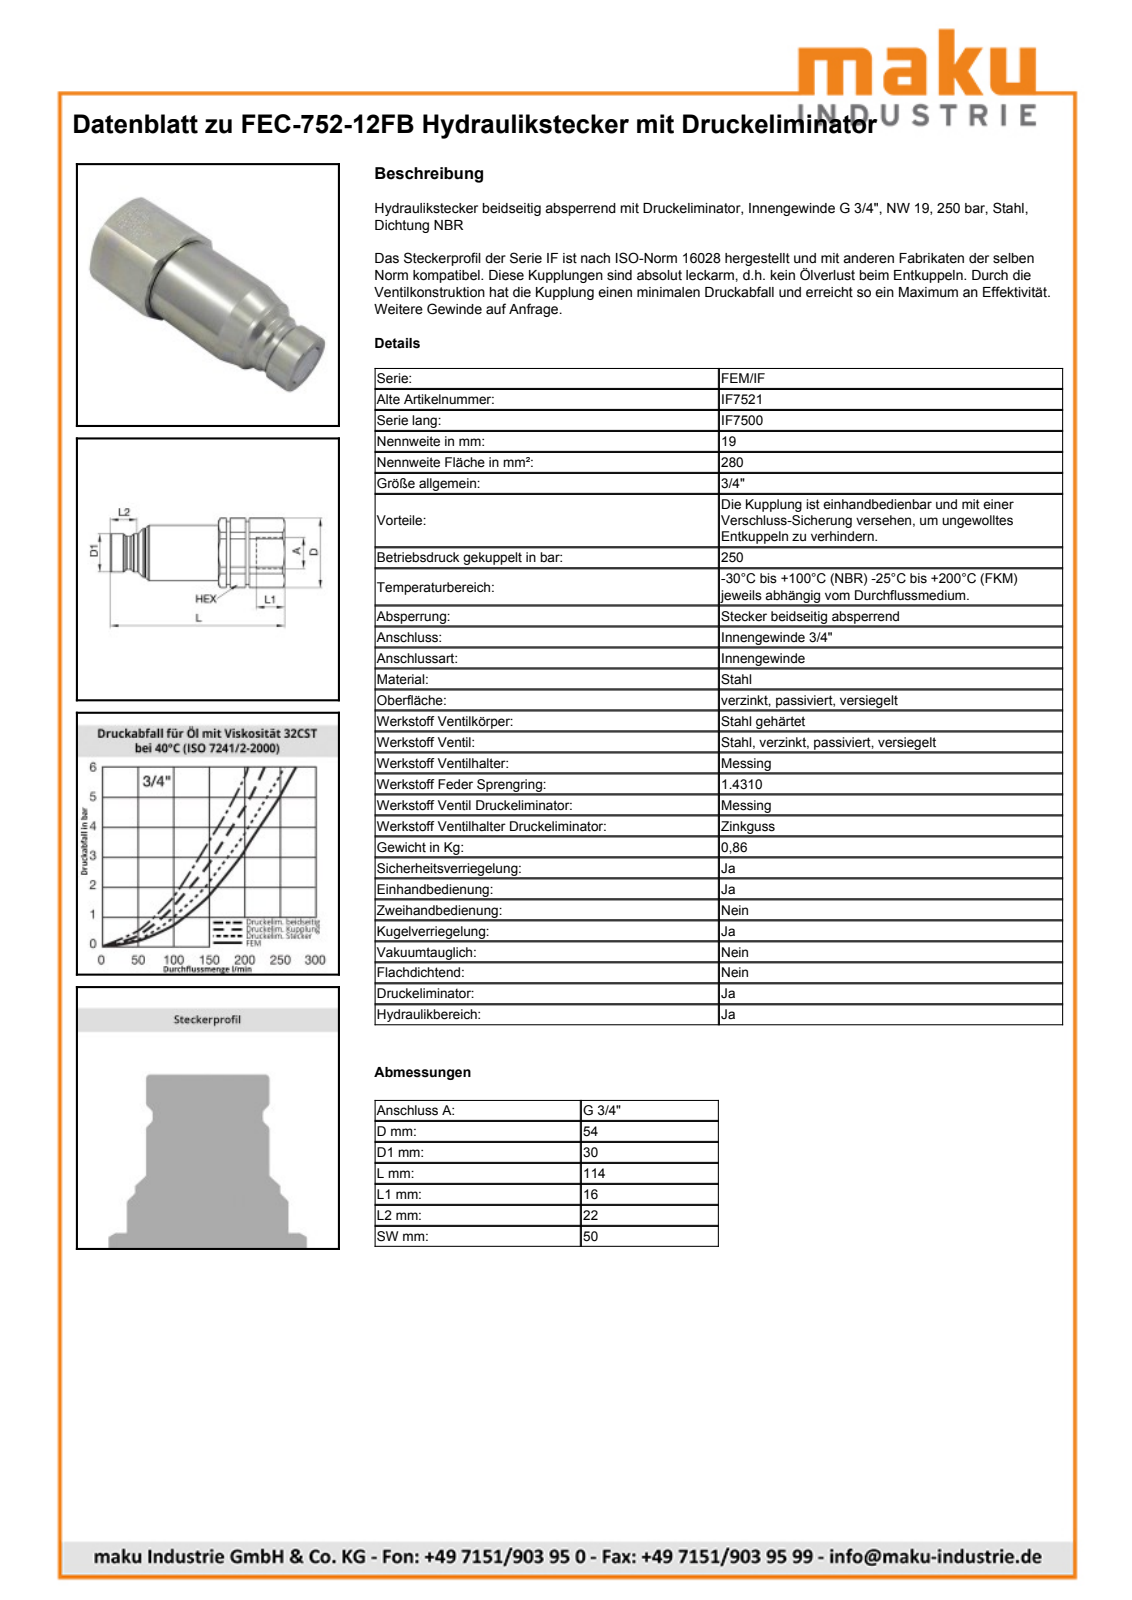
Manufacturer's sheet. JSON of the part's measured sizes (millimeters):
{"part_name": "FEC-752-12FB", "step_written_by": "SolidWorks 2009 (AUTOMOTIVE_DESIGN)", "units": "millimeters", "bodies": {"solids": 1, "faces": 167, "planar": 51, "cylindrical": 45, "other": 71}, "overall_size": [113.55, 54, 50], "volume_mm3": 161048, "surface_area_mm2": 22694, "round_holes": [[1.5, 1], [20.7, 1], [23.5, 1], [24.12, 1], [44.2, 1]], "round_bosses_or_shafts": [[45, 1], [42, 1], [38.05, 1], [29.95, 1], [26.9, 1]], "partial_cylinders_radius": [[0.5, 8], [6, 1], [14.55, 1], [27, 1]], "face_to_face_distances": [50, 25.09, 9.91, 35, 78.44, 88.35, 113.44, 78.55, 88.46, 113.55]}
